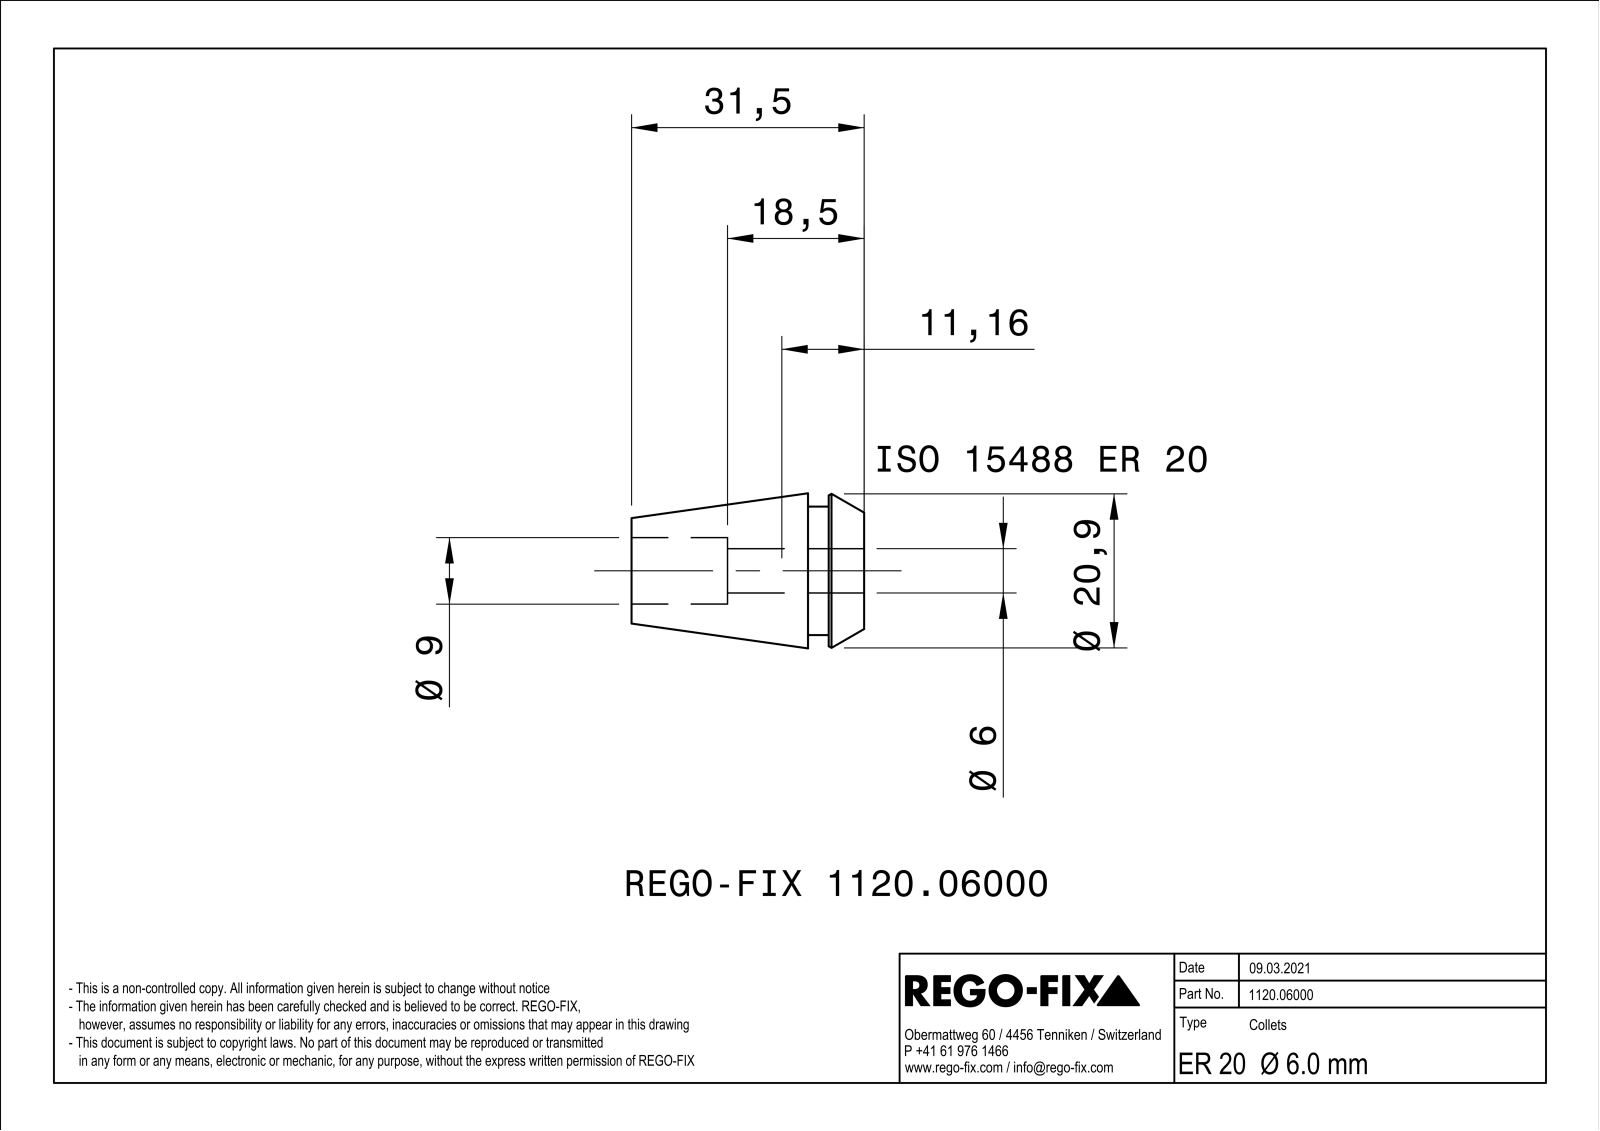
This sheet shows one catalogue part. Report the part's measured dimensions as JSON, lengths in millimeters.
{"part_name": "NOCUT", "step_written_by": "SIEMENS PLM Software Solid Edge ST10 (AUTOMOTIVE_DESIGN)", "units": "millimeters", "bodies": {"solids": 1, "faces": 257, "planar": 104, "cylindrical": 41, "other": 112}, "overall_size": [31.5, 20.99, 20.99], "volume_mm3": 5356, "surface_area_mm2": 6433, "round_holes": [[9, 1]], "round_bosses_or_shafts": [[17.4, 1]], "partial_cylinders_radius": [[40, 8], [3, 1]], "face_to_face_distances": [0.6, 0.62, 0.58, 7.6, 4.8, 2.8, 31.5, 26.7, 23.9, 27]}
